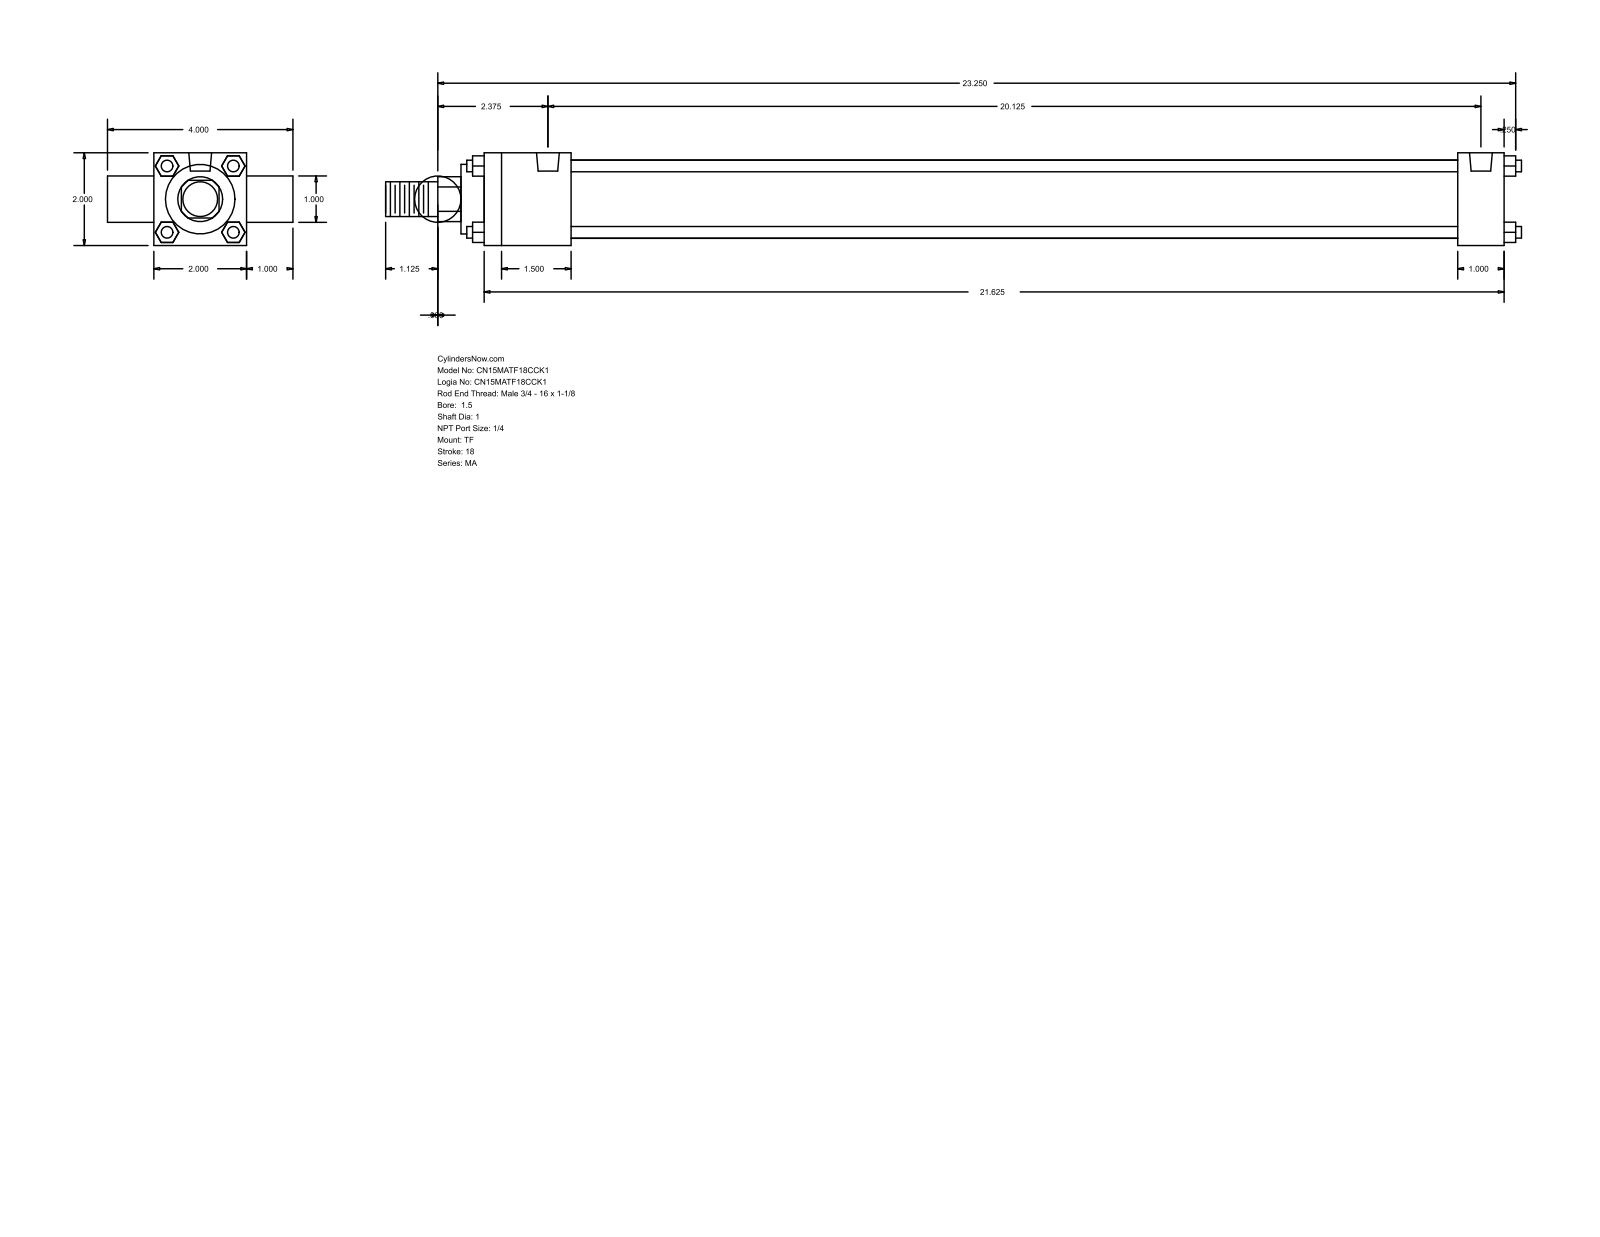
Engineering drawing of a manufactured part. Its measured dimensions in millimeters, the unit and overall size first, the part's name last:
Units: millimetres
Overall size (bounding box): 622.3 × 101.6 × 50.8
Round holes (diameter × count): ⌀7.94 ×3, ⌀12.49 ×2
Round bosses / shafts (diameter × count): ⌀6.35 ×4, ⌀25.4 ×2, ⌀42.93 ×1, ⌀38.1 ×1, ⌀19.05 ×1
Partial cylindrical surfaces — rounded edges, fillets, slot ends (radius × count): R12.29 ×1
Main face-to-face distances: 50.8, 25.4, 558.8, 76.2, 6.35, 47.63, 533.4, 485.77, 511.17, 571.5
Hole centre spacings: 511.17
Bodies: 0 solids, 120 faces (92 planar, 28 cylindrical, 0 other)
Part name (STEP PRODUCT): MA_TF__0150_1
STEP written by: GSSL Pune (CONFIG_CONTROL_DESIGN)
